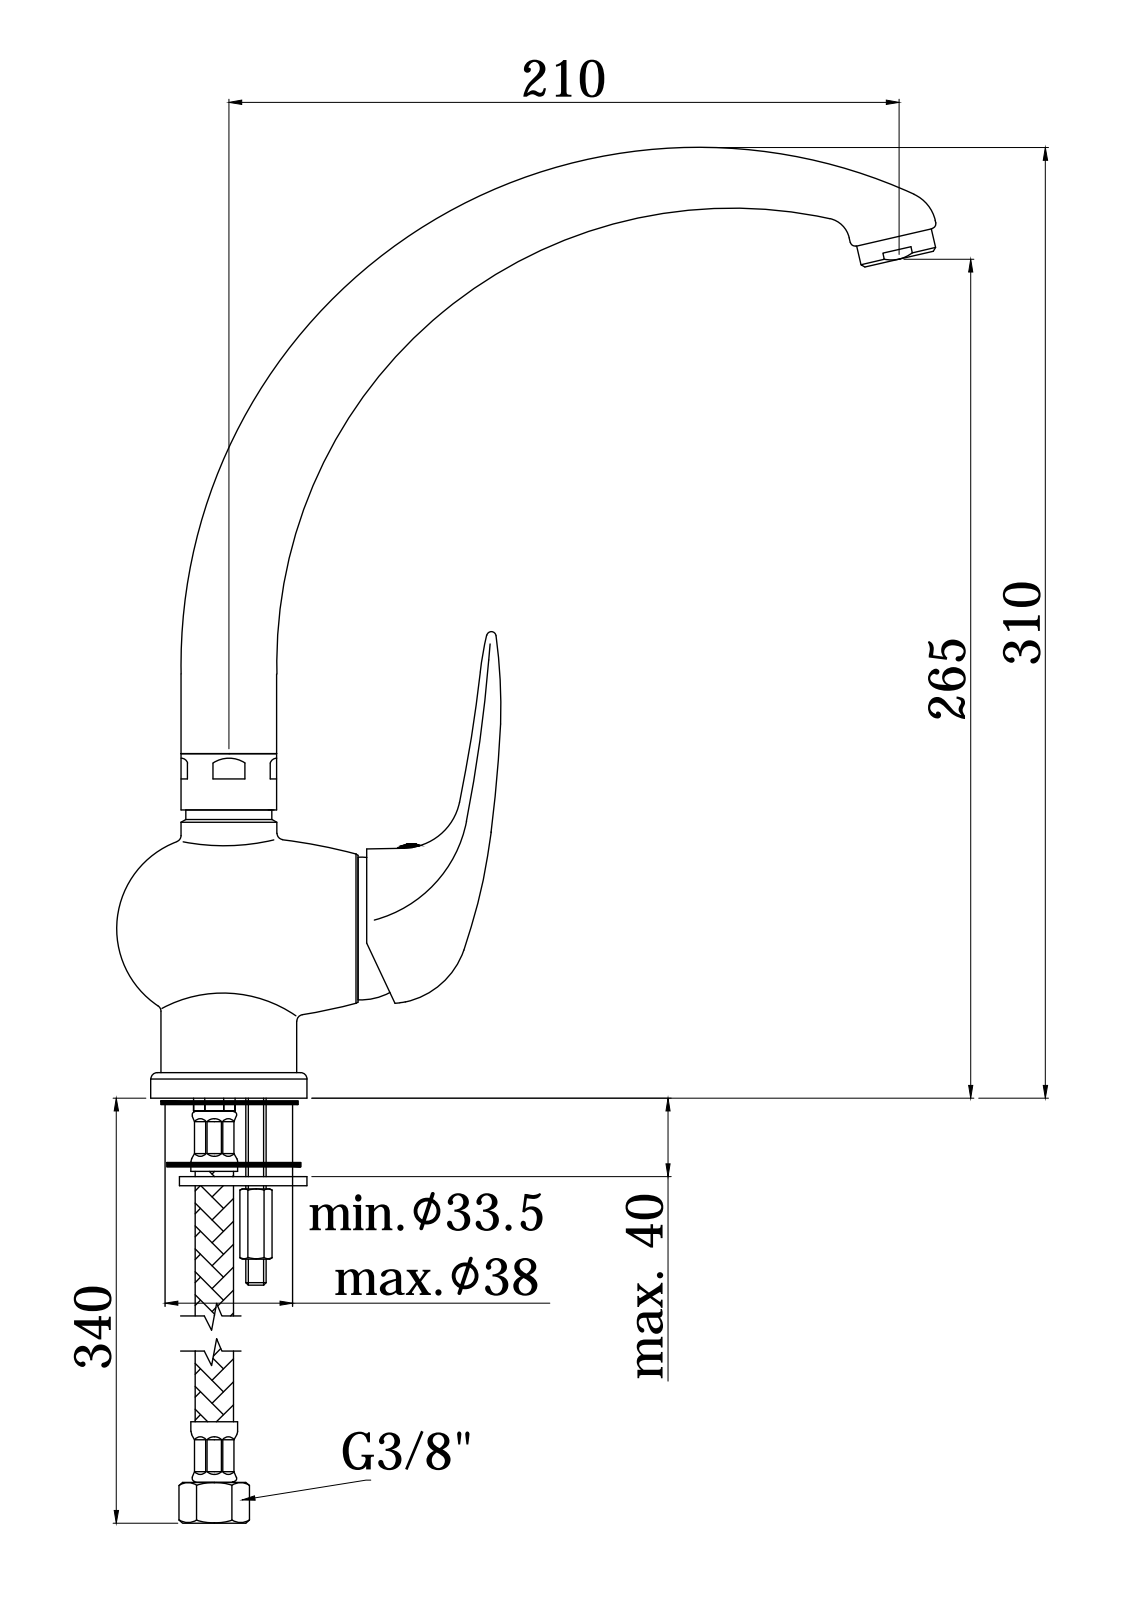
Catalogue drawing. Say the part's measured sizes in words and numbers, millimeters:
The part is named "DU181CR". Its 3-D file was written by "CREO PARAMETRIC BY PTC INC, 2020044 (CONFIG_CONTROL_DESIGN)". It is 3 solids with 2517 faces: 1929 planar, 318 cylindrical and 270 other. Overall it measures 303.7 by 249.67 by 122.95 millimeters. Its volume is 251 100 cubic millimeters and its surface area 131 252 square millimeters. Round holes: 4 of diameter 8, 3 of diameter 11, 2 of diameter 5.25, 2 of diameter 6.5, 2 of diameter 7, 2 of diameter 9, 2 of diameter 11.7, 2 of diameter 21, 2 of diameter 24.5, 2 of diameter 35, 1 of diameter 3.5, 1 of diameter 4. Round bosses or shafts: 1 of diameter 50, 1 of diameter 43, 1 of diameter 39.5, 1 of diameter 37.4, 1 of diameter 36.7, 1 of diameter 32.1, 1 of diameter 30, 1 of diameter 25.8. Partial cylindrical surfaces (rounded edges, fillets, slot ends): 37 of radius 0.5, 24 of radius 0.2, 2 of radius 1.5, 2 of radius 15, 2 of radius 24, 2 of radius 24.5, 1 of radius 1, 1 of radius 3.25. The main face-to-face distances are 6, 2, 4, 32.2, 2.5, 18.9, 1, 13.3, 10, 8.5. The hole center spacings are 13.04, 13.46, 9.7, 0.54, 1.51, 2, 8.6, 9.6.
